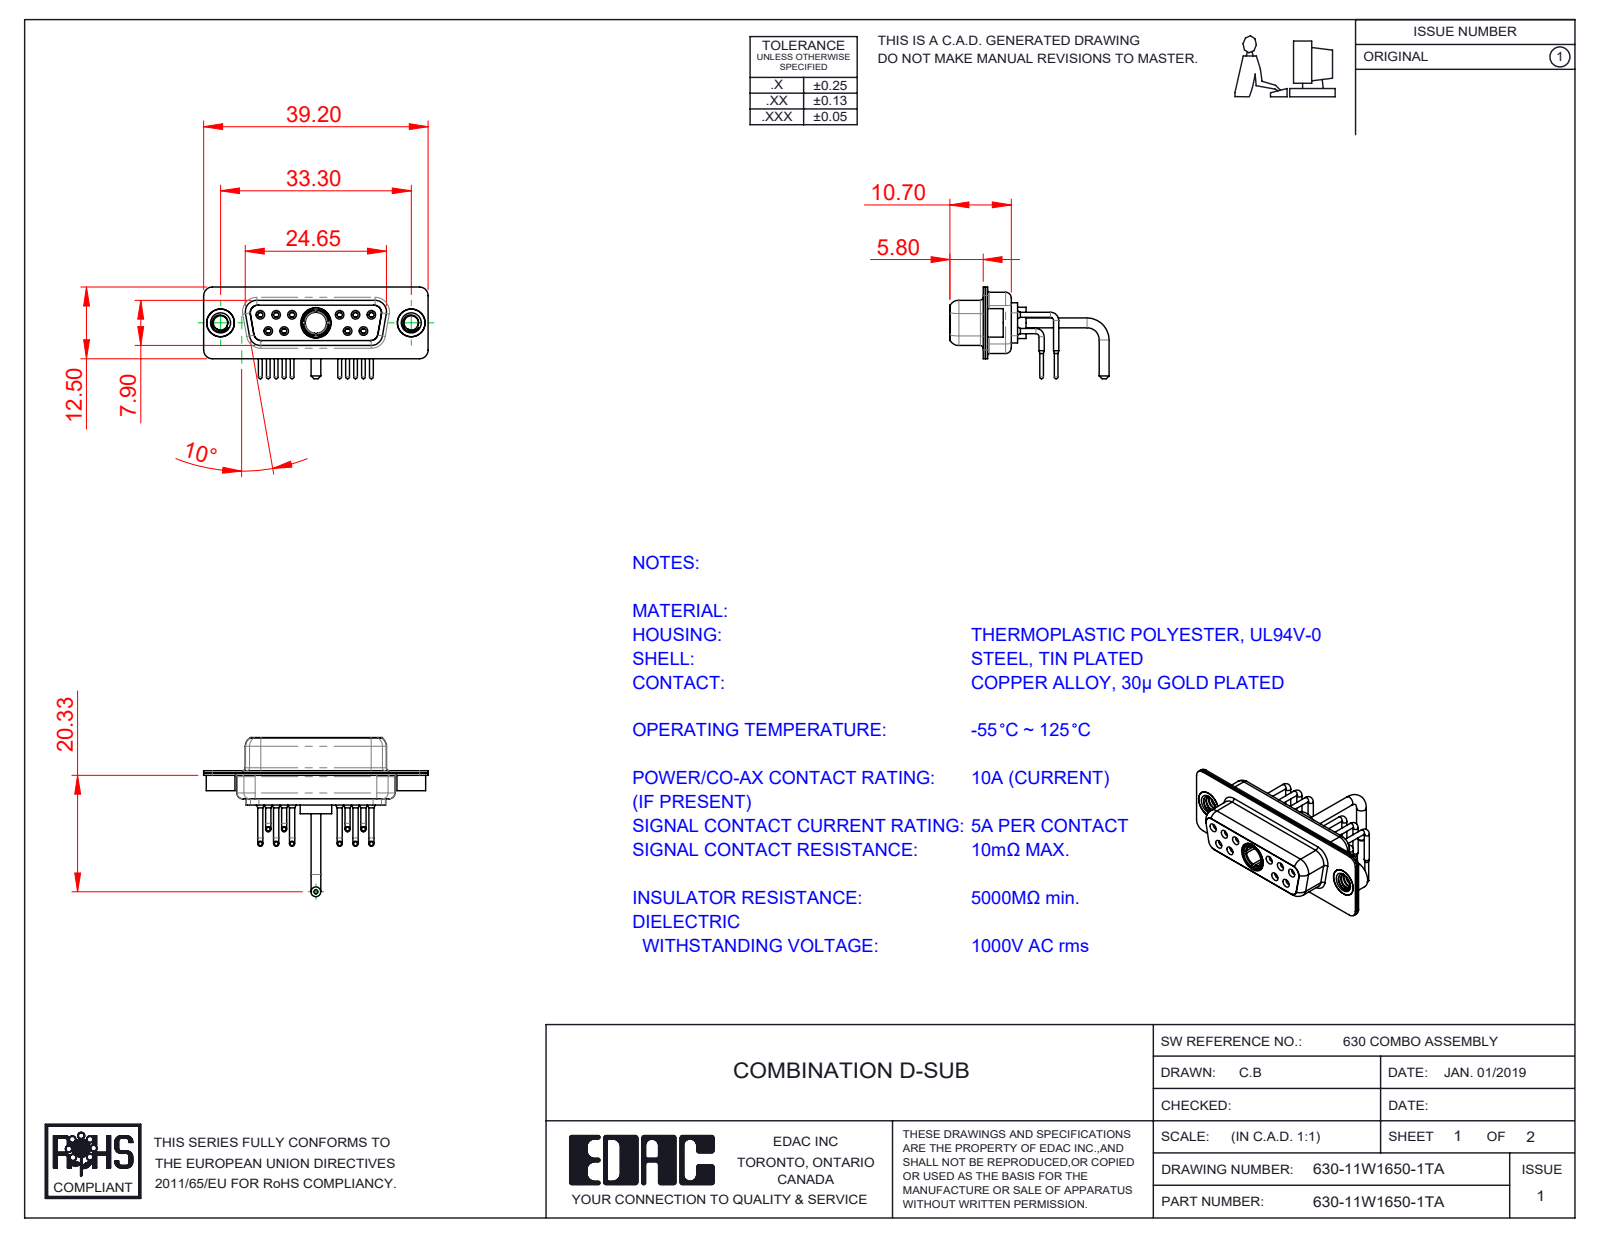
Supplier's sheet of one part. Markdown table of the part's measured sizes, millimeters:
| quantity | value |
| --- | --- |
| part name | 630Combo Contact Row 2; 630Combo Contact Row 1; 630Combo Shell Front_15 Contacts; Power Socket_Ext 10A RA (+4 more) |
| STEP written by | SolidWorks 2020 (CONFIG_CONTROL_DESIGN) |
| units | millimeters |
| bodies | 17 solids, 881 faces (246 planar, 390 cylindrical, 245 other) |
| overall size | 39.2 × 27.78 × 16 |
| volume | 2 598 mm³ |
| surface area | 6 263 mm² |
| round holes (diameter × count) | 0.9 × 10, 1.1 × 10, 1.5 × 10, 2 × 10, 1.7 × 6, 1.6 × 4, 4.85 × 3, 2.5 × 2, 4 × 2, 4.05 × 2, 3.7 × 1, 5.3 × 1 |
| round bosses / shafts (diameter × count) | 0.9 × 10, 0.65 × 10, 1.6 × 6, 5 × 2, 4.95 × 2, 4.8 × 2, 1.7 × 2, 5.5 × 1 |
| partial cylindrical surfaces (radius × count) | 1.5 × 16, 1.35 × 12, 2 × 12, 1.6 × 8, 0.25 × 4, 0.5 × 4, 0.6 × 4, 0.65 × 4 |
| main face-to-face distances | 0.4, 1.4, 0.45, 8.45, 1.8, 8.9, 0.8, 6.2, 7.05, 1.85 |
| hole center spacings | 3.16, 2.77, 13.85, 11.08, 16.62, 5.03, 5.04, 5.54 |
